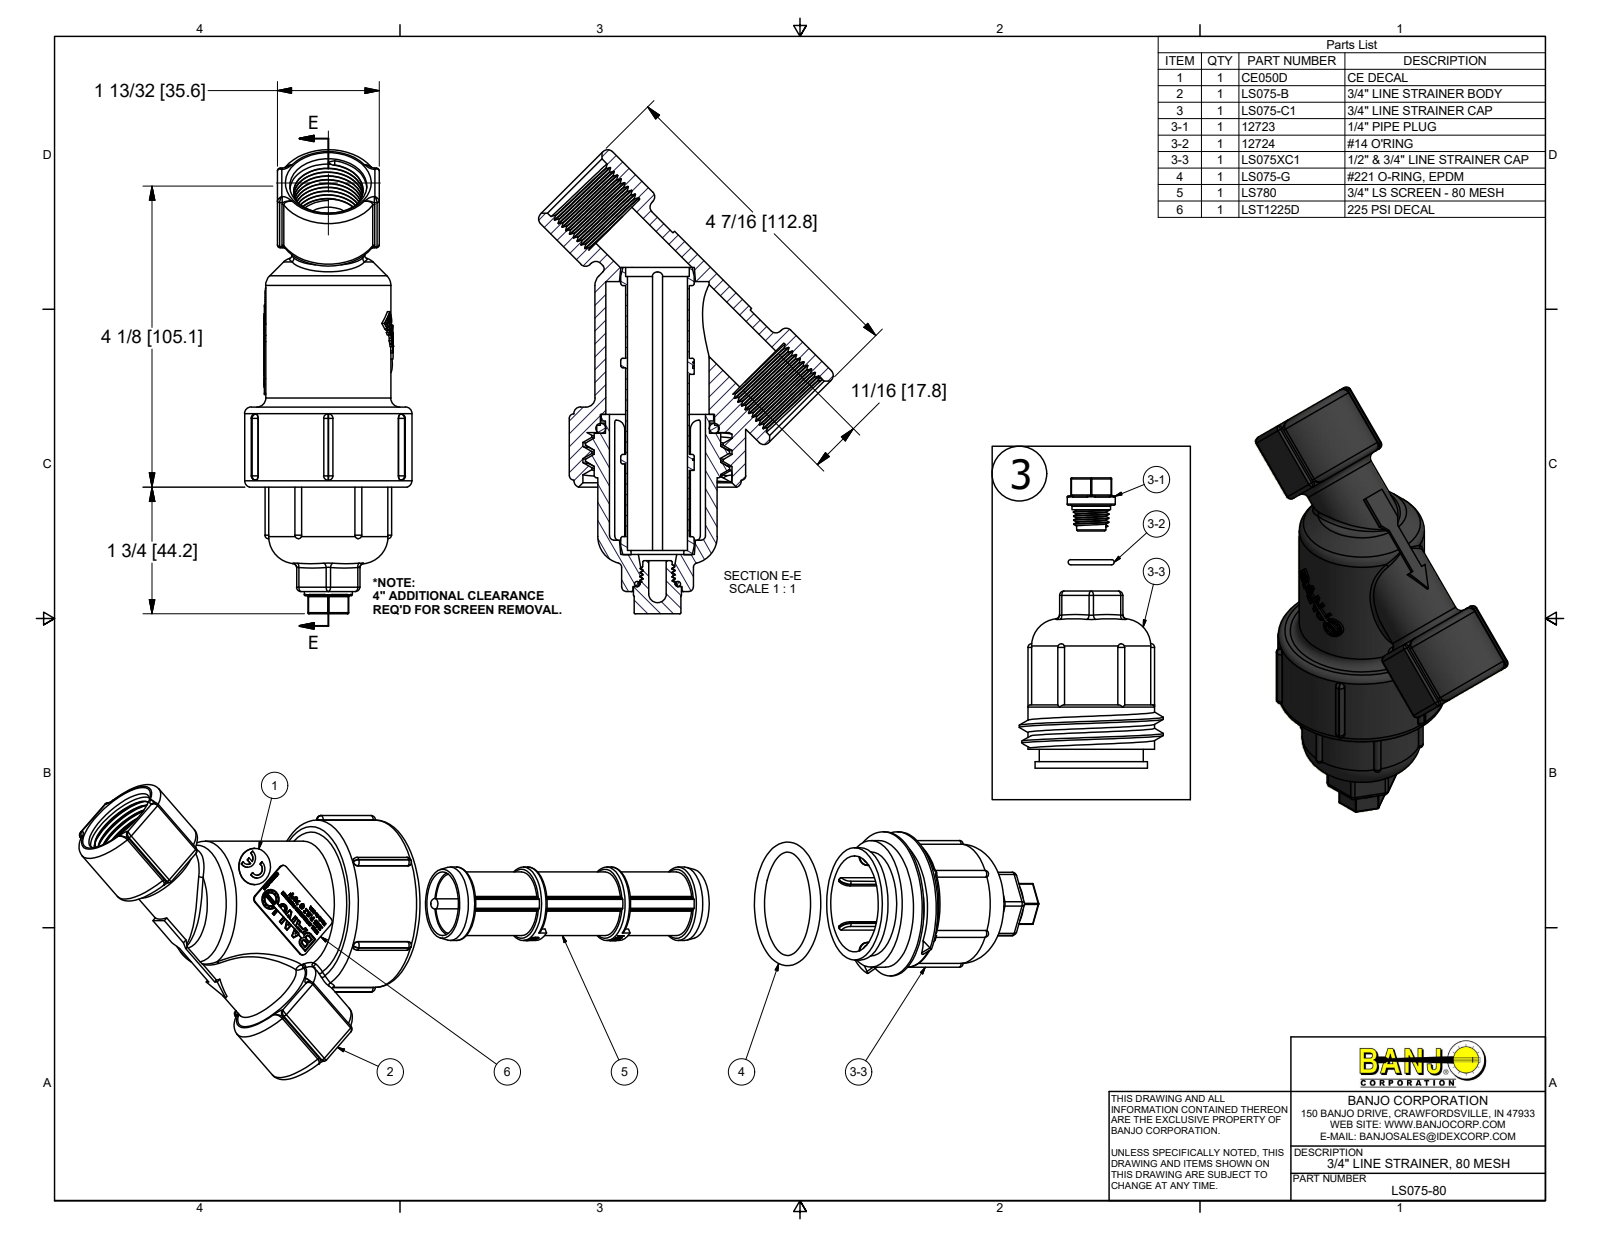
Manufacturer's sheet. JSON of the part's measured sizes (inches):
{"part_name": "LS075-80; CE050D; LS075-B; LS075-C1 (+6 more)", "step_written_by": "Autodesk Inventor 2018 (AUTOMOTIVE_DESIGN)", "units": "inches", "bodies": {"solids": 8, "faces": 2283, "planar": 1126, "cylindrical": 388, "other": 769}, "overall_size": [21.064, 21.064, 2.3], "volume_in3": 17.38, "surface_area_in2": 584.5, "round_holes": [[0.181, 2], [0.257, 2], [0.24, 1], [0.675, 1], [0.7, 1], [0.725, 1], [0.825, 1], [1.32, 1], [1.42, 1], [1.57, 1], [1.671, 1], [1.809, 1]], "round_bosses_or_shafts": [[0.27, 2], [2.3, 1], [1.981, 1], [1.74, 1], [1.72, 1], [1.64, 1], [1.545, 1], [1.43, 1]], "partial_cylinders_radius": [[0.06, 67], [0.03, 35], [0.015, 26], [0.125, 8], [0.05, 6], [0.026, 4], [0.033, 4], [0.063, 4]], "face_to_face_distances": [0.25, 1.4, 0.16, 1.56, 3.75, 0.07, 0.26, 2.085, 2.075, 1.825], "hole_center_spacings": [0.638]}
